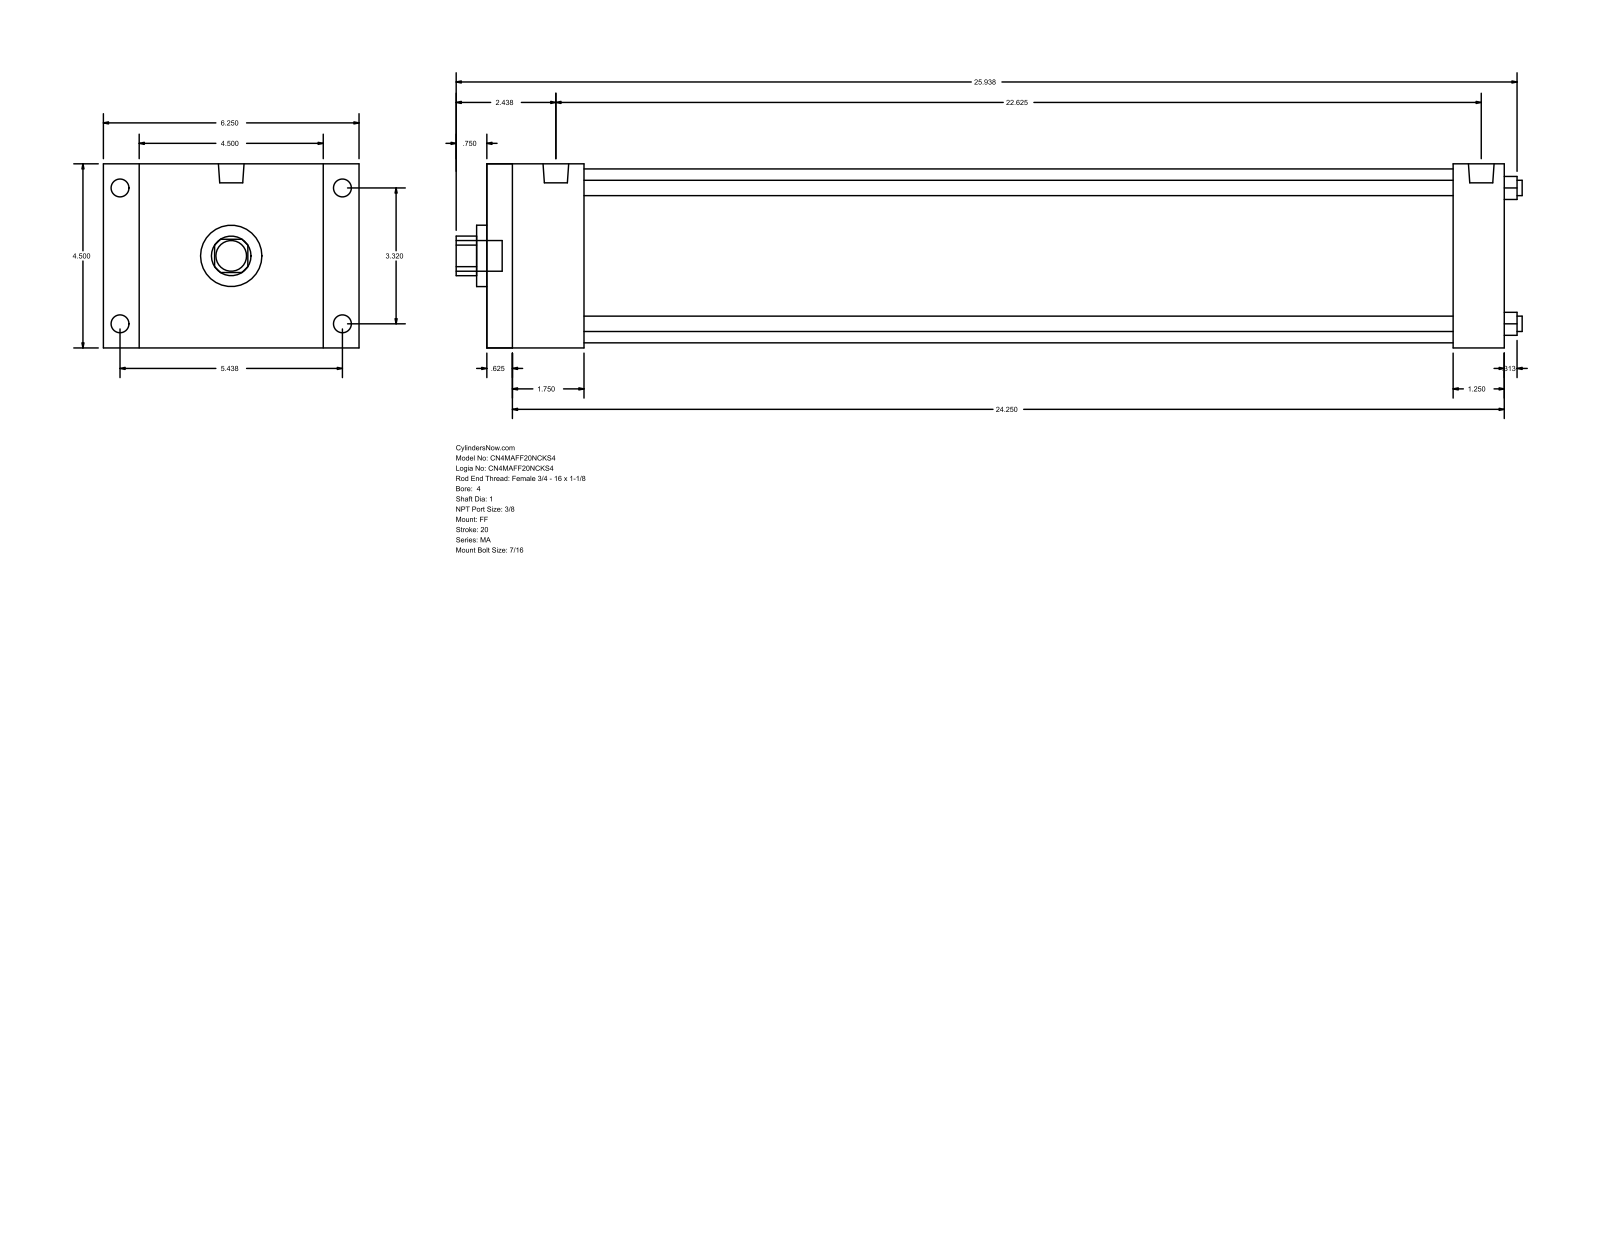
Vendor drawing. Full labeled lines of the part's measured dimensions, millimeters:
Part name (STEP PRODUCT): MA_FF__0400_1
STEP written by: GSSL Pune (CONFIG_CONTROL_DESIGN)
Units: millimetres
Bodies: 0 solids, 92 faces (64 planar, 28 cylindrical, 0 other)
Overall size (bounding box): 661.99 × 158.75 × 114.3
Round holes (diameter × count): ⌀9.53 ×4, ⌀25.4 ×1, ⌀38.1 ×1, ⌀107.95 ×1
Round bosses / shafts (diameter × count): ⌀11.11 ×8, ⌀15.93 ×2, ⌀19.05 ×1
Partial cylindrical surfaces — rounded edges, fillets, slot ends (radius × count): R12.29 ×1
Main face-to-face distances: 114.3, 631.83, 15.87, 615.96, 22.23, 136.53, 600.07, 584.2, 31.76, 60.33
Hole centre spacings: 59.62, 84.32, 119.25
